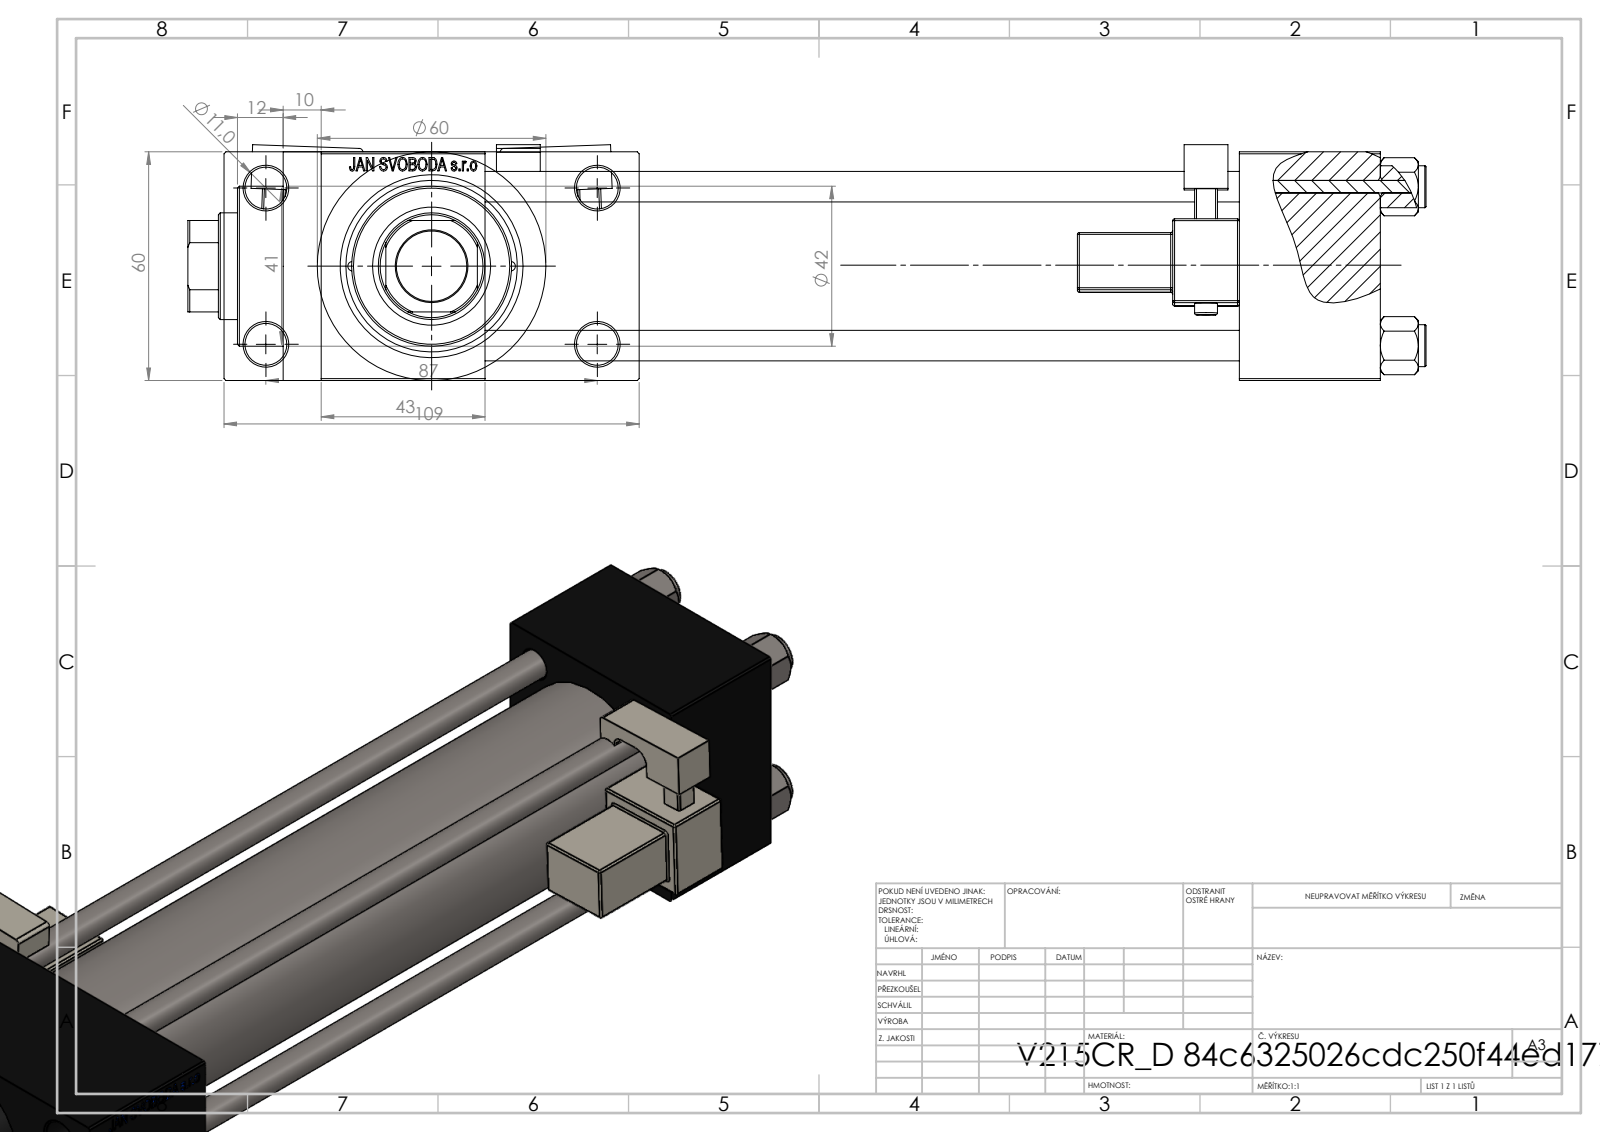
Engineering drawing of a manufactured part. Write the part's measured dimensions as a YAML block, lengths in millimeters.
part_name: "NUT_M5_D; V215CR_VCP_D; V215CR_MSU; V215CR_D_TYCINKA (+2 more)"
step_written_by: "SolidWorks 2019 (CONFIG_CONTROL_DESIGN)"
units: millimeters
bodies: {solids: 13, faces: 1268, planar: 560, cylindrical: 152, other: 556}
overall_size: [325, 109, 61.9]
volume: 740592
surface_area: 205377
round_holes:
  - {diameter: 8, count: 4}
  - {diameter: 11, count: 4}
  - {diameter: 2.5, count: 2}
  - {diameter: 7, count: 2}
  - {diameter: 16.66, count: 2}
  - {diameter: 24, count: 2}
  - {diameter: 18.5, count: 1}
  - {diameter: 28, count: 1}
  - {diameter: 31, count: 1}
  - {diameter: 40, count: 1}
  - {diameter: 45, count: 1}
round_bosses_or_shafts:
  - {diameter: 11, count: 4}
  - {diameter: 6, count: 2}
  - {diameter: 60, count: 1}
  - {diameter: 46, count: 1}
  - {diameter: 42, count: 1}
partial_cylinders:
  - {radius: 0.5, count: 48}
  - {radius: 1, count: 2}
  - {radius: 2.5, count: 2}
  - {radius: 4, count: 2}
  - {radius: 13.5, count: 1}
face_to_face_distances: [60, 198, 24.5, 84.5, 37, 235, 278, 241, 43, 109]
hole_center_spacings: [20.85, 22.65, 29.49, 30.62, 41.7, 46.53, 47.15, 48.09]
